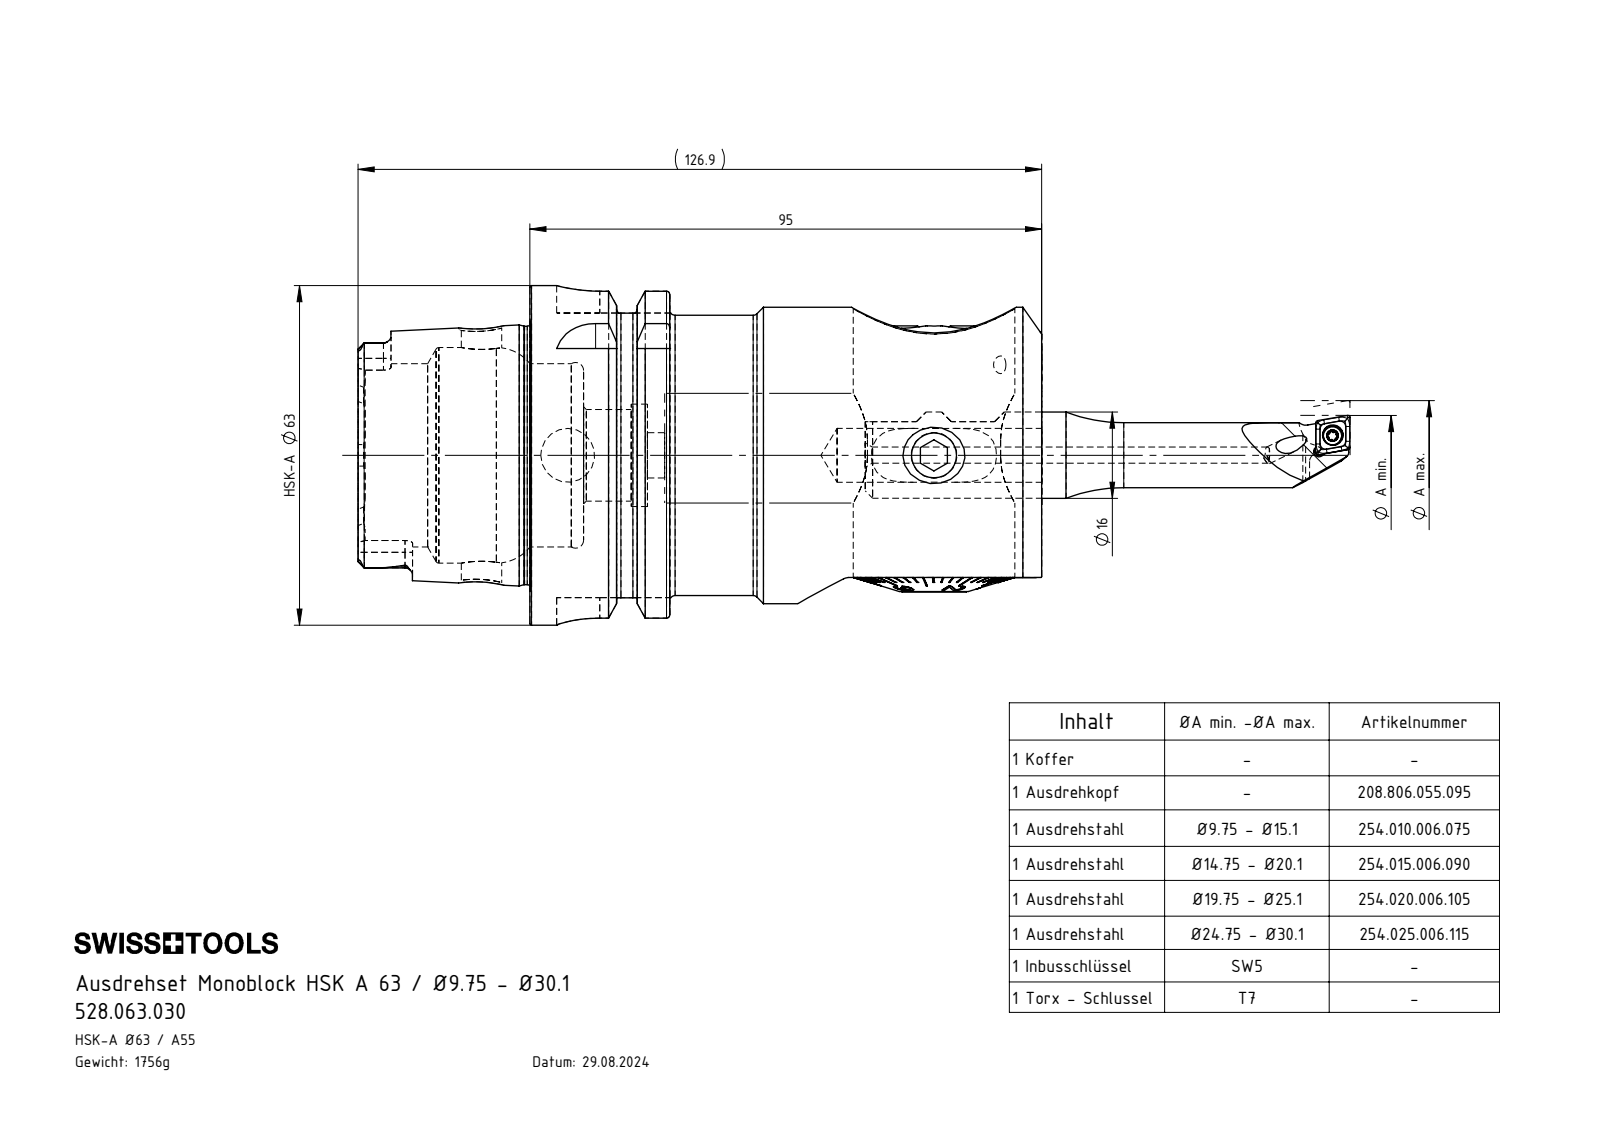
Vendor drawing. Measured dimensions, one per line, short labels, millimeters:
name: B10-WCA.K11.075; B10-WCA.K11.075_C; ISO 4026 - M10 x 16_PreviewCfg; ISO 4026 - M10 x 8 (+8 more)
written by: SolidWorks 2022 (AUTOMOTIVE_DESIGN)
unit: mm
bodies: 28 solids, 1422 faces (518 planar, 339 cylindrical, 565 other)
size: 238.4 × 126.9 × 63
volume: 274 659 mm³; area: 79 657 mm²
holes: 8× ⌀3, 4× ⌀2.05, 4× ⌀2.8, 4× ⌀3.85, 3× ⌀2, 3× ⌀8.5, 2× ⌀10, 1× ⌀1.6, 1× ⌀2.1, 1× ⌀3.3, 1× ⌀4.2, 1× ⌀7.5
bosses: 4× ⌀16, 4× ⌀3.4, 4× ⌀2.5, 3× ⌀10, 2× ⌀18, 1× ⌀63, 1× ⌀55, 1× ⌀54.95
rounds: 24× R0.21, 17× R0.36, 10× R1.4, 7× R0.36, 6× R0.34, 6× R0.59, 6× R8, 4× R0.5
face distances: 95, 31.9, 126.9, 16, 57.85, 25.95, 69.05, 41.85, 9.95, 85.05
hole spacings: 14.5, 3.89, 3.99, 7.25, 42.76, 0.33, 3.88, 3.98
